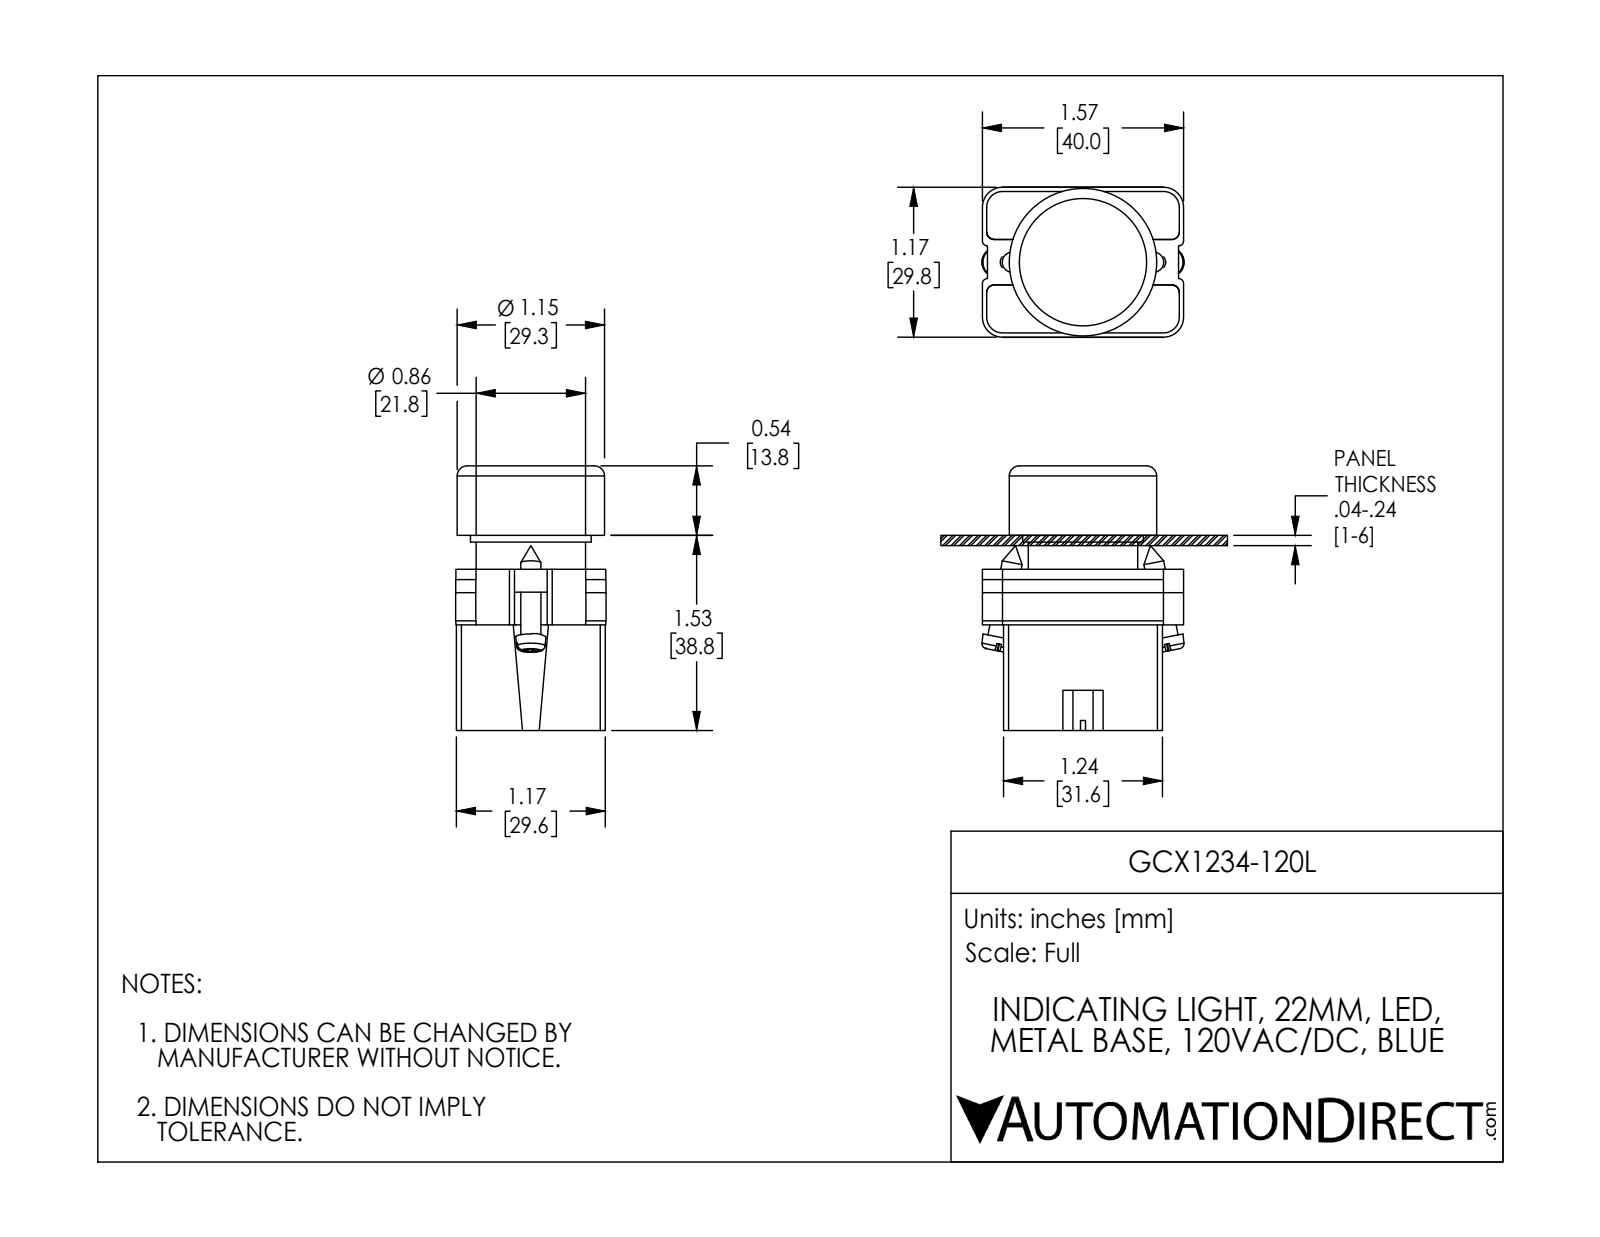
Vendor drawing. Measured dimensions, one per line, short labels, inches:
name: ecx1029; GCX1234-120L; ECX1050; GCX1234L OPERATOR
written by: SolidWorks 2016 (AUTOMOTIVE_DESIGN)
unit: in
bodies: 7 solids, 339 faces (178 planar, 134 cylindrical, 27 other)
size: 2.071 × 1.581 × 1.177
volume: 2.268 in³; area: 31.19 in²
holes: 2× ⌀0.124, 2× ⌀0.13, 1× ⌀0.197, 1× ⌀0.469, 1× ⌀0.852, 1× ⌀0.878, 1× ⌀0.888, 1× ⌀1.102
bosses: 4× ⌀0.157, 1× ⌀1.154, 1× ⌀1.092, 1× ⌀0.945, 1× ⌀0.856, 1× ⌀0.78, 1× ⌀0.504
rounds: 24× R0.059, 12× R0.041, 12× R0.124, 12× R0.157, 8× R0.039, 2× R0.128, 1× R0.392, 1× R0.398
face distances: 0.86, 1.244, 0.827, 1.687, 1.136, 0.033, 1.963, 0.276, 0.031, 1.165
